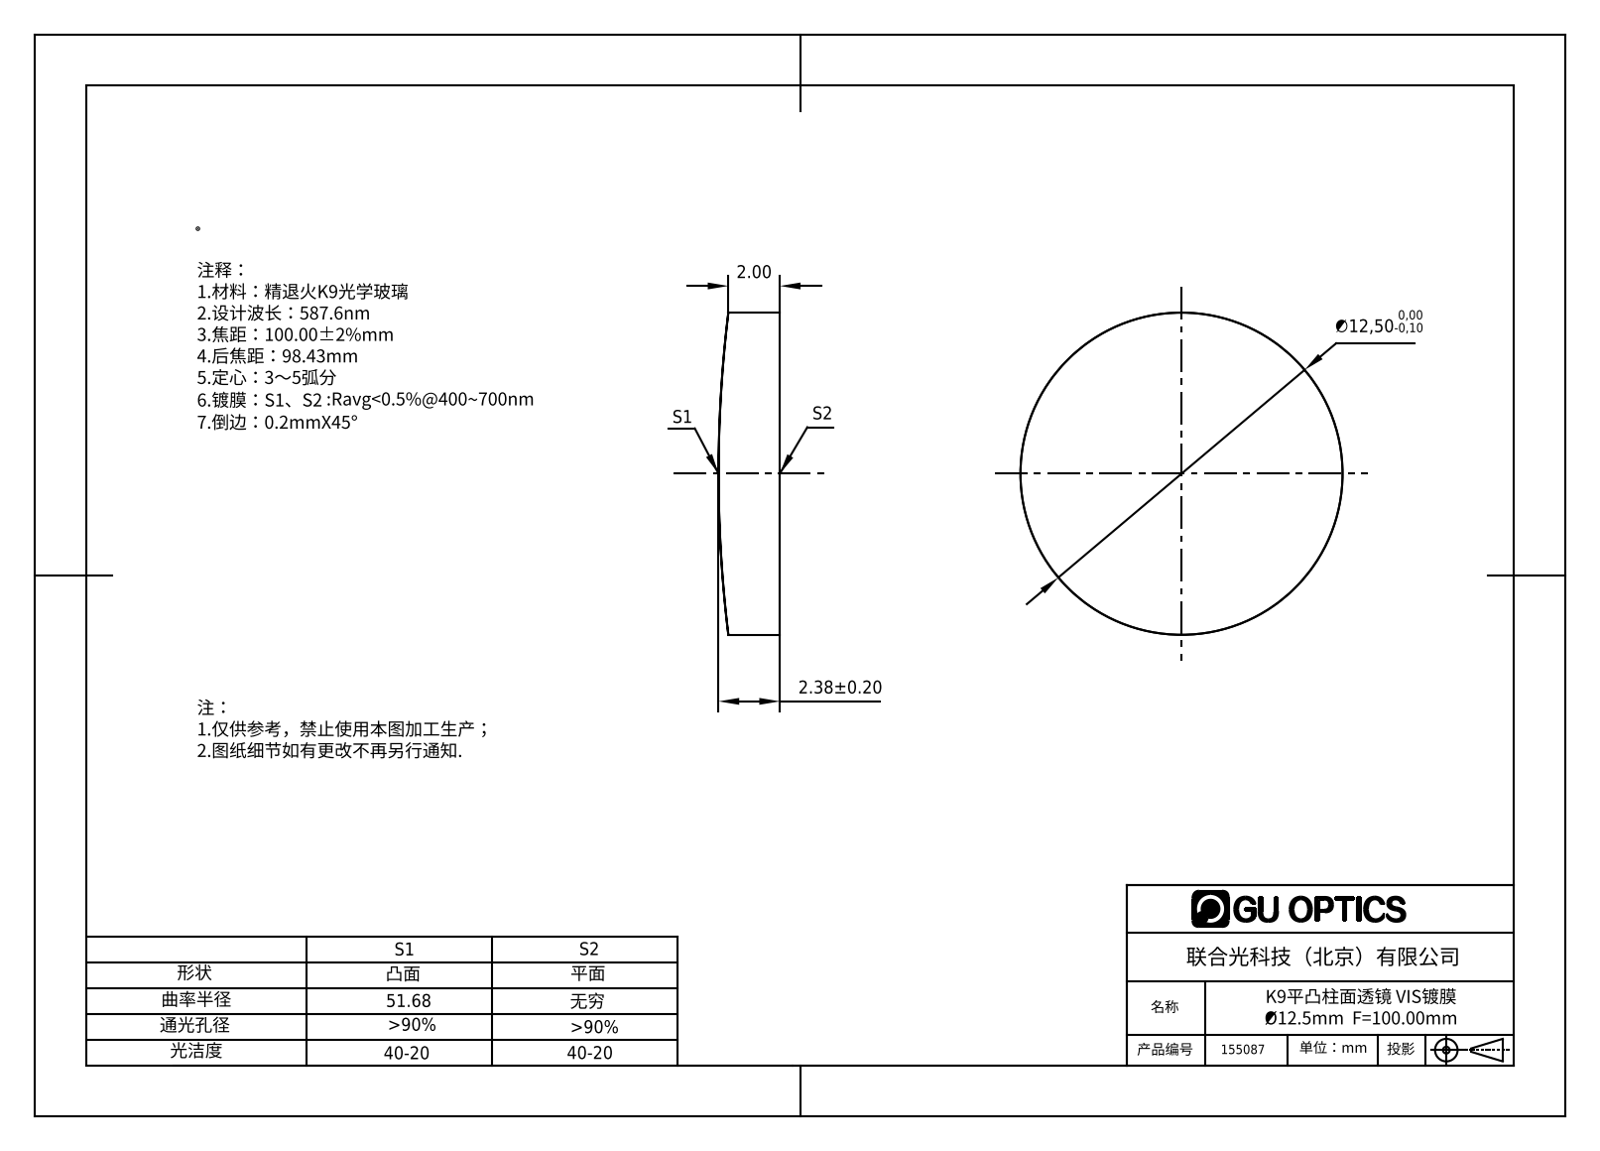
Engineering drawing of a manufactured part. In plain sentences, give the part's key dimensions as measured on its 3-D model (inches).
The part is named "155021". Its 3-D file was written by "SolidWorks 2016 (AUTOMOTIVE_DESIGN)". It is 1 solid with 4 faces: 1 planar, 3 cylindrical and 0 other. Overall it measures 0.492 by 0.492 by 0.094 inches. Its volume is 0.017 cubic inches and its surface area 0.515 square inches. Round bosses or shafts: 1 of diameter 0.492. Partial cylindrical surfaces (rounded edges, fillets, slot ends): 1 of radius 2.035.
